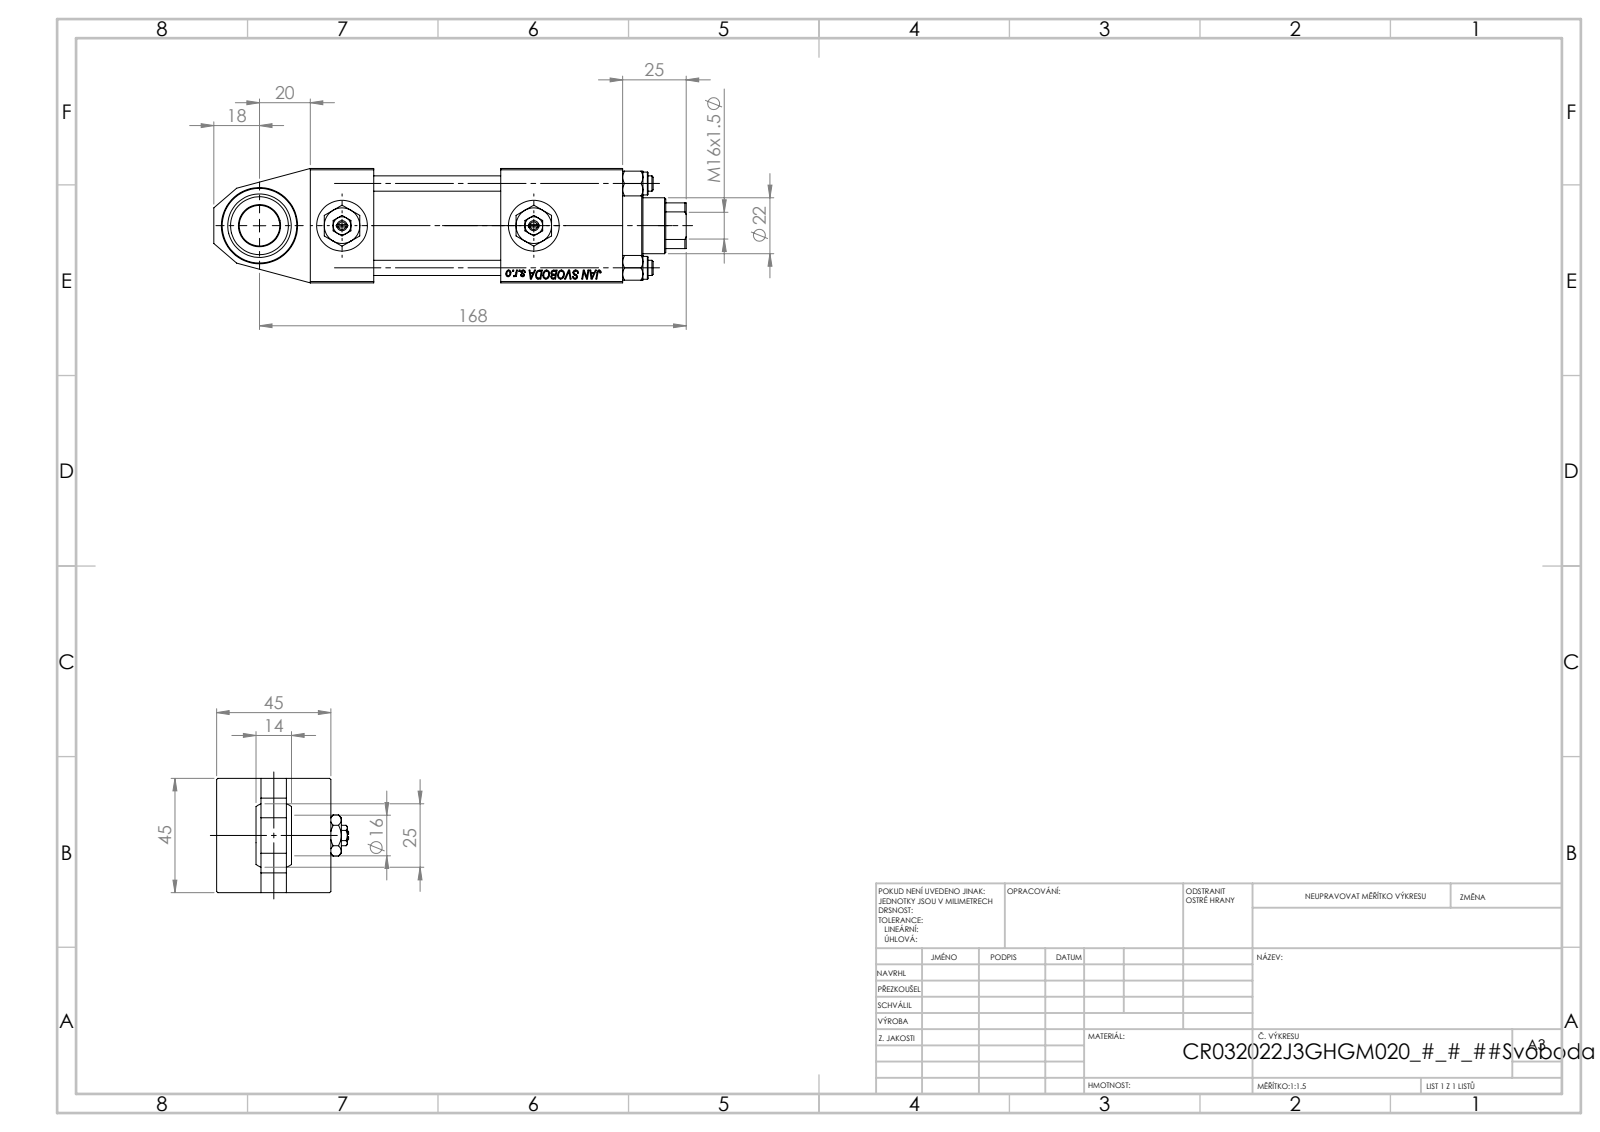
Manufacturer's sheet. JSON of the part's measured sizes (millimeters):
{"part_name": "NUT_M5_J; V215CR_J_VNITRNI_KROUZEK; V215CR_TYCINKA_J; V215CR_J_Body (+3 more)", "step_written_by": "SolidWorks 2019 (CONFIG_CONTROL_DESIGN)", "units": "millimeters", "bodies": {"solids": 14, "faces": 1244, "planar": 562, "cylindrical": 100, "other": 582}, "overall_size": [186, 52, 45], "volume_mm3": 220459, "surface_area_mm2": 81030, "round_holes": [[6, 4], [2.5, 2], [7, 2], [13.16, 2], [20, 2], [10.5, 1], [16, 1], [22, 1], [24, 1], [25, 1], [30, 1], [32, 1]], "round_bosses_or_shafts": [[9, 4], [38, 1], [34, 1]], "partial_cylinders_radius": [[10.5, 1]], "face_to_face_distances": [45, 25, 17.5, 27.5, 17.3, 50, 123, 2, 75, 44.8], "hole_center_spacings": [16.7, 23.48, 33.2, 35.47, 14.75, 46.95, 29.5, 32.5]}
